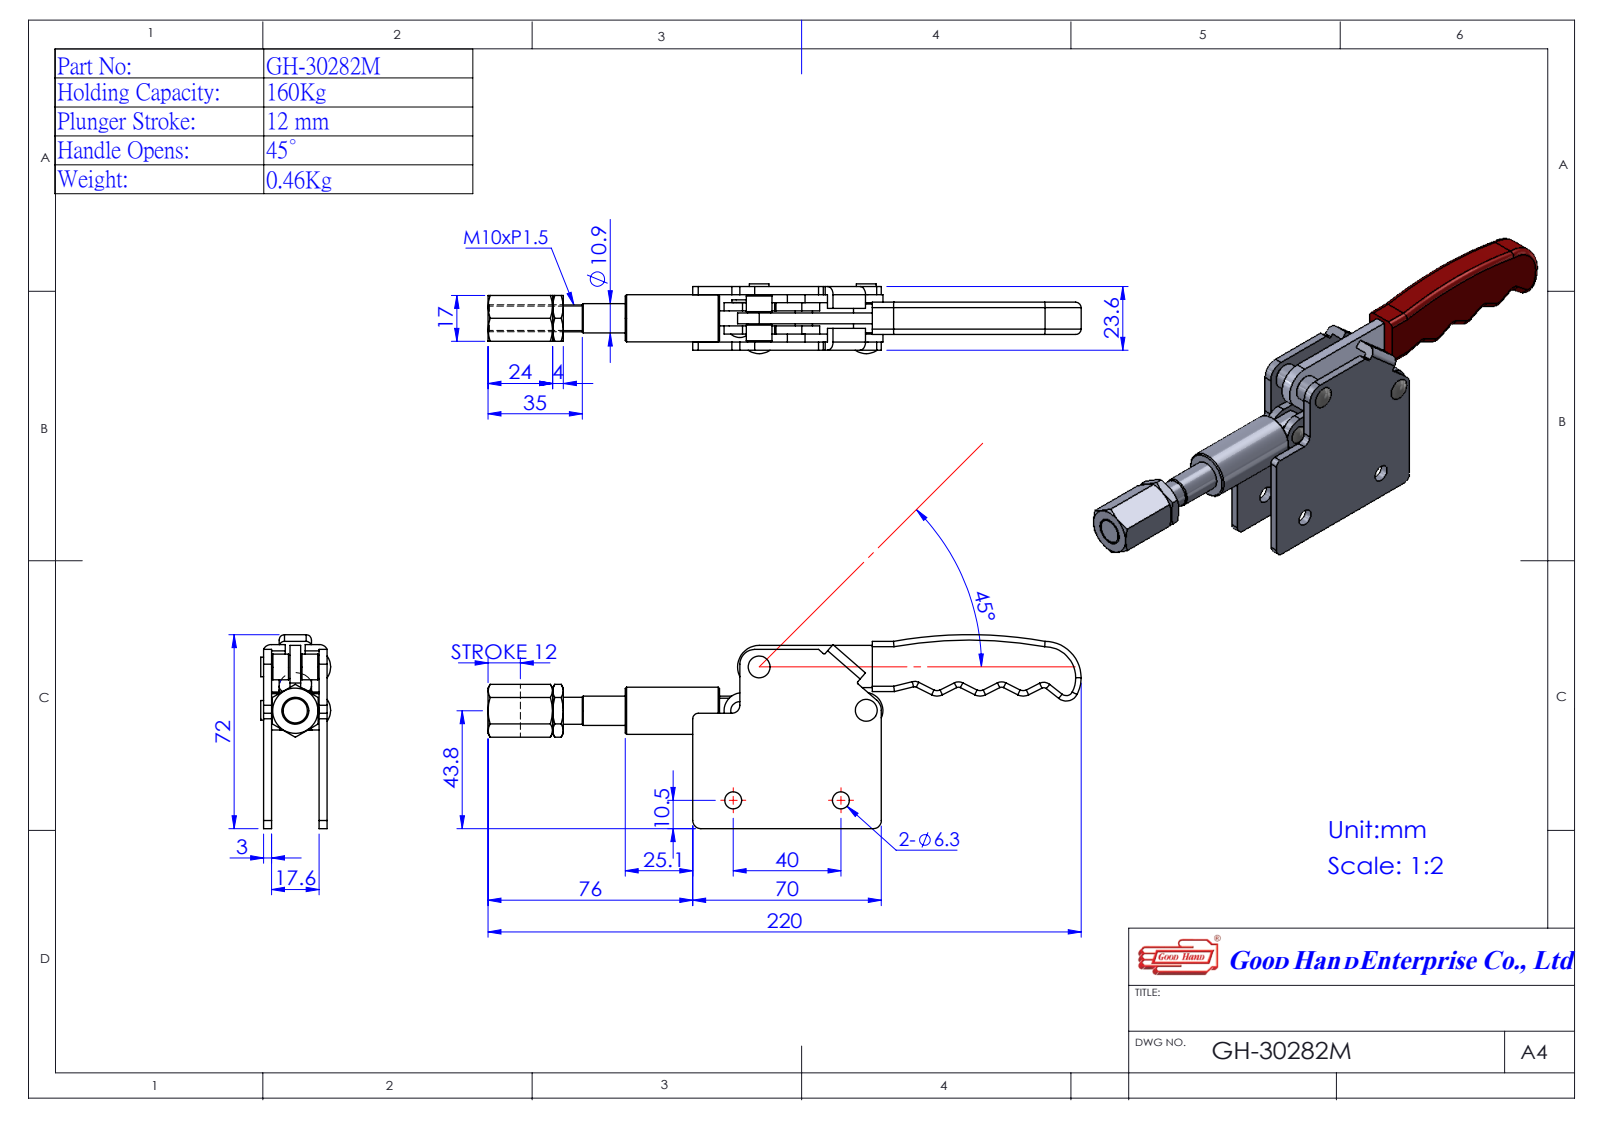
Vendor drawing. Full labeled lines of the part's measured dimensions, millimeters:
Part name (STEP PRODUCT): Group2^GH-30282M(簡化)-1; 1302DM01-1^GH-30282M(簡化)-1; Group3^GH-30282M(簡化)-1; GH-30282M(簡化)-1 (+3 more)
STEP written by: SolidWorks 2016 (AUTOMOTIVE_DESIGN)
Units: millimetres
Bodies: 7 solids, 221 faces (98 planar, 103 cylindrical, 20 other)
Overall size (bounding box): 220.18 × 72.09 × 25.9
Volume: 71 889 mm³ · Surface area: 41 540 mm²
Round holes (diameter × count): ⌀4 ×4, ⌀6.3 ×2, ⌀10 ×1, ⌀10.9 ×1
Round bosses / shafts (diameter × count): ⌀7.3 ×2, ⌀17.5 ×1, ⌀10 ×1, ⌀9.5 ×1, ⌀5.83 ×1, ⌀4.83 ×1, ⌀4 ×1
Partial cylindrical surfaces — rounded edges, fillets, slot ends (radius × count): R0.5 ×4, R1.5 ×4, R4.5 ×4, R6.75 ×4, R3 ×3, R2 ×2, R5.5 ×2, R1 ×1
Main face-to-face distances: 3, 20.6, 17.6, 23.6, 4, 14.8, 5.8, 17.8, 2.8, 6.8
Hole centre spacings: 17.74, 23.15, 23.65, 23.73, 33.34, 34.7, 35.45, 40
